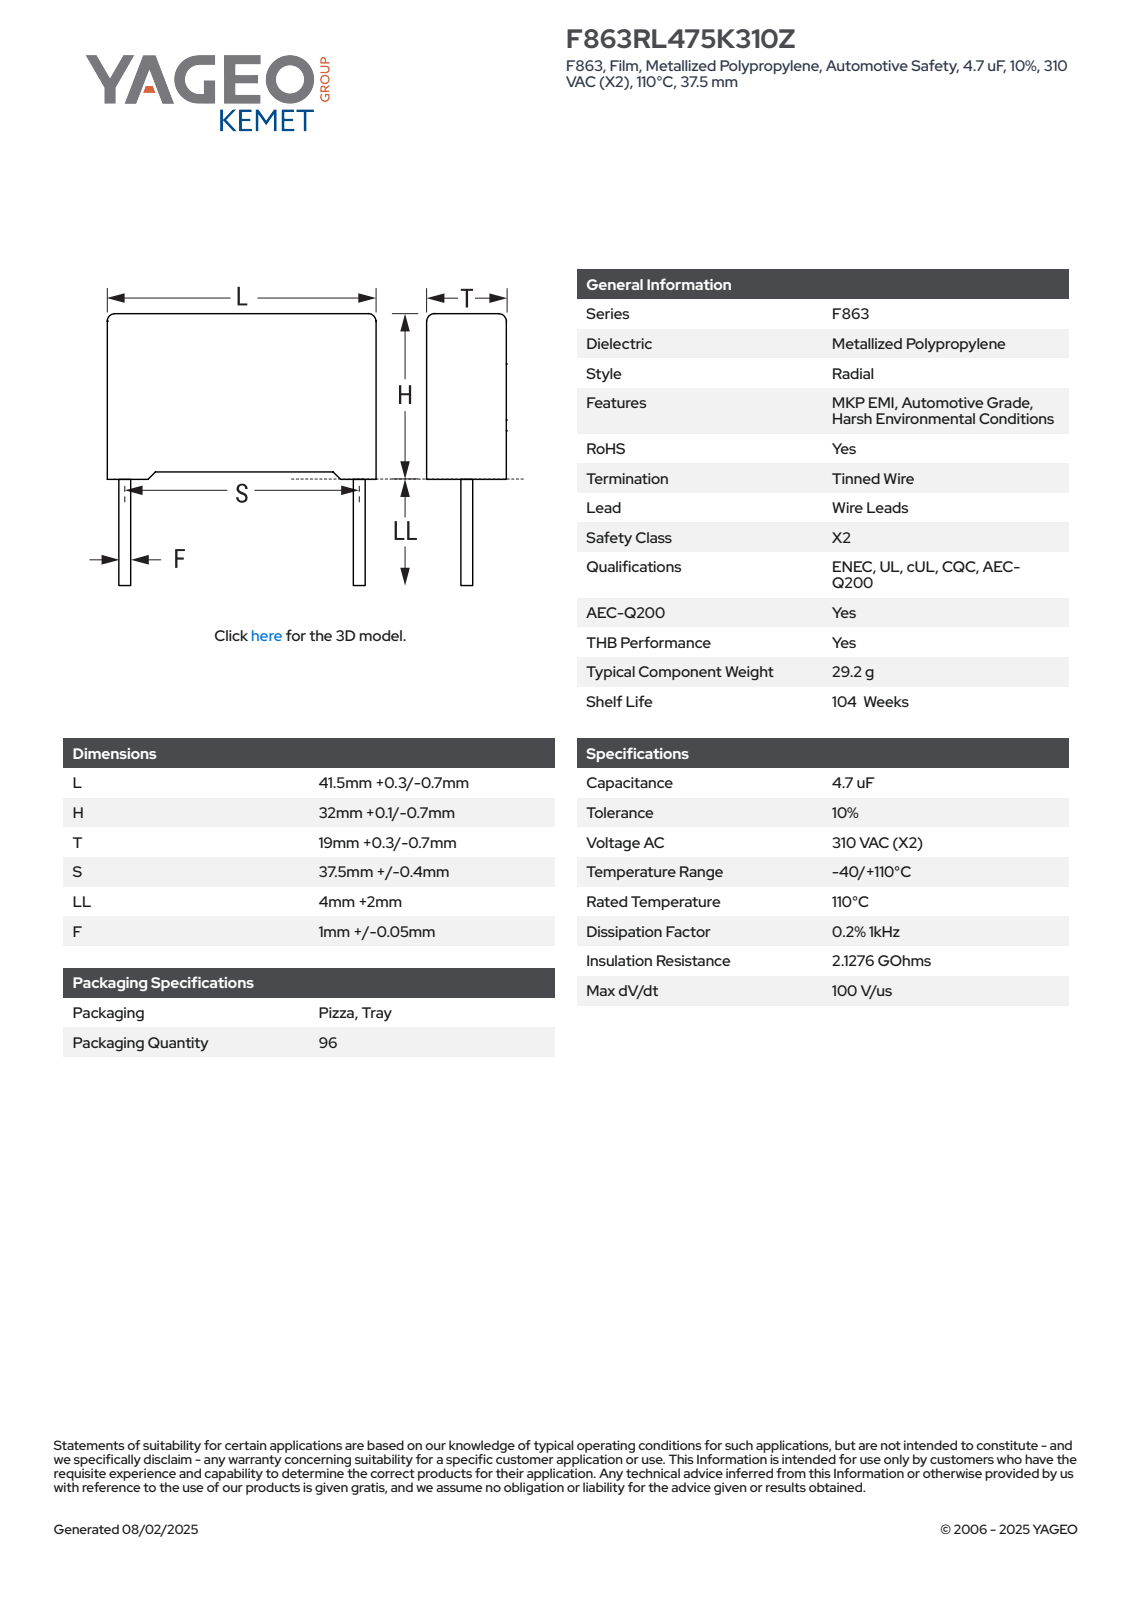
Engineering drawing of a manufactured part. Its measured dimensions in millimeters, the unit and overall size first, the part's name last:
Units: millimetres
Overall size (bounding box): 41.8 × 38.1 × 19.3
Round bosses / shafts (diameter × count): ⌀1.05 ×2
Partial cylindrical surfaces — rounded edges, fillets, slot ends (radius × count): R0.5 ×4
Main face-to-face distances: 19.3, 30.99, 41.8, 0.36, 31.35, 0.75, 1.11, 32.1, 1.39, 19.31
Volume: 25 124 mm³ · Surface area: 5 651 mm²
Bodies: 4 solids, 85 faces (77 planar, 8 cylindrical, 0 other)
Part name (STEP PRODUCT): CFR_RB2_41.5X32X19_L41.8H32.1T19.3S37.5LL6F1.05
STEP written by: SolidWorks 2021 (AUTOMOTIVE_DESIGN)
